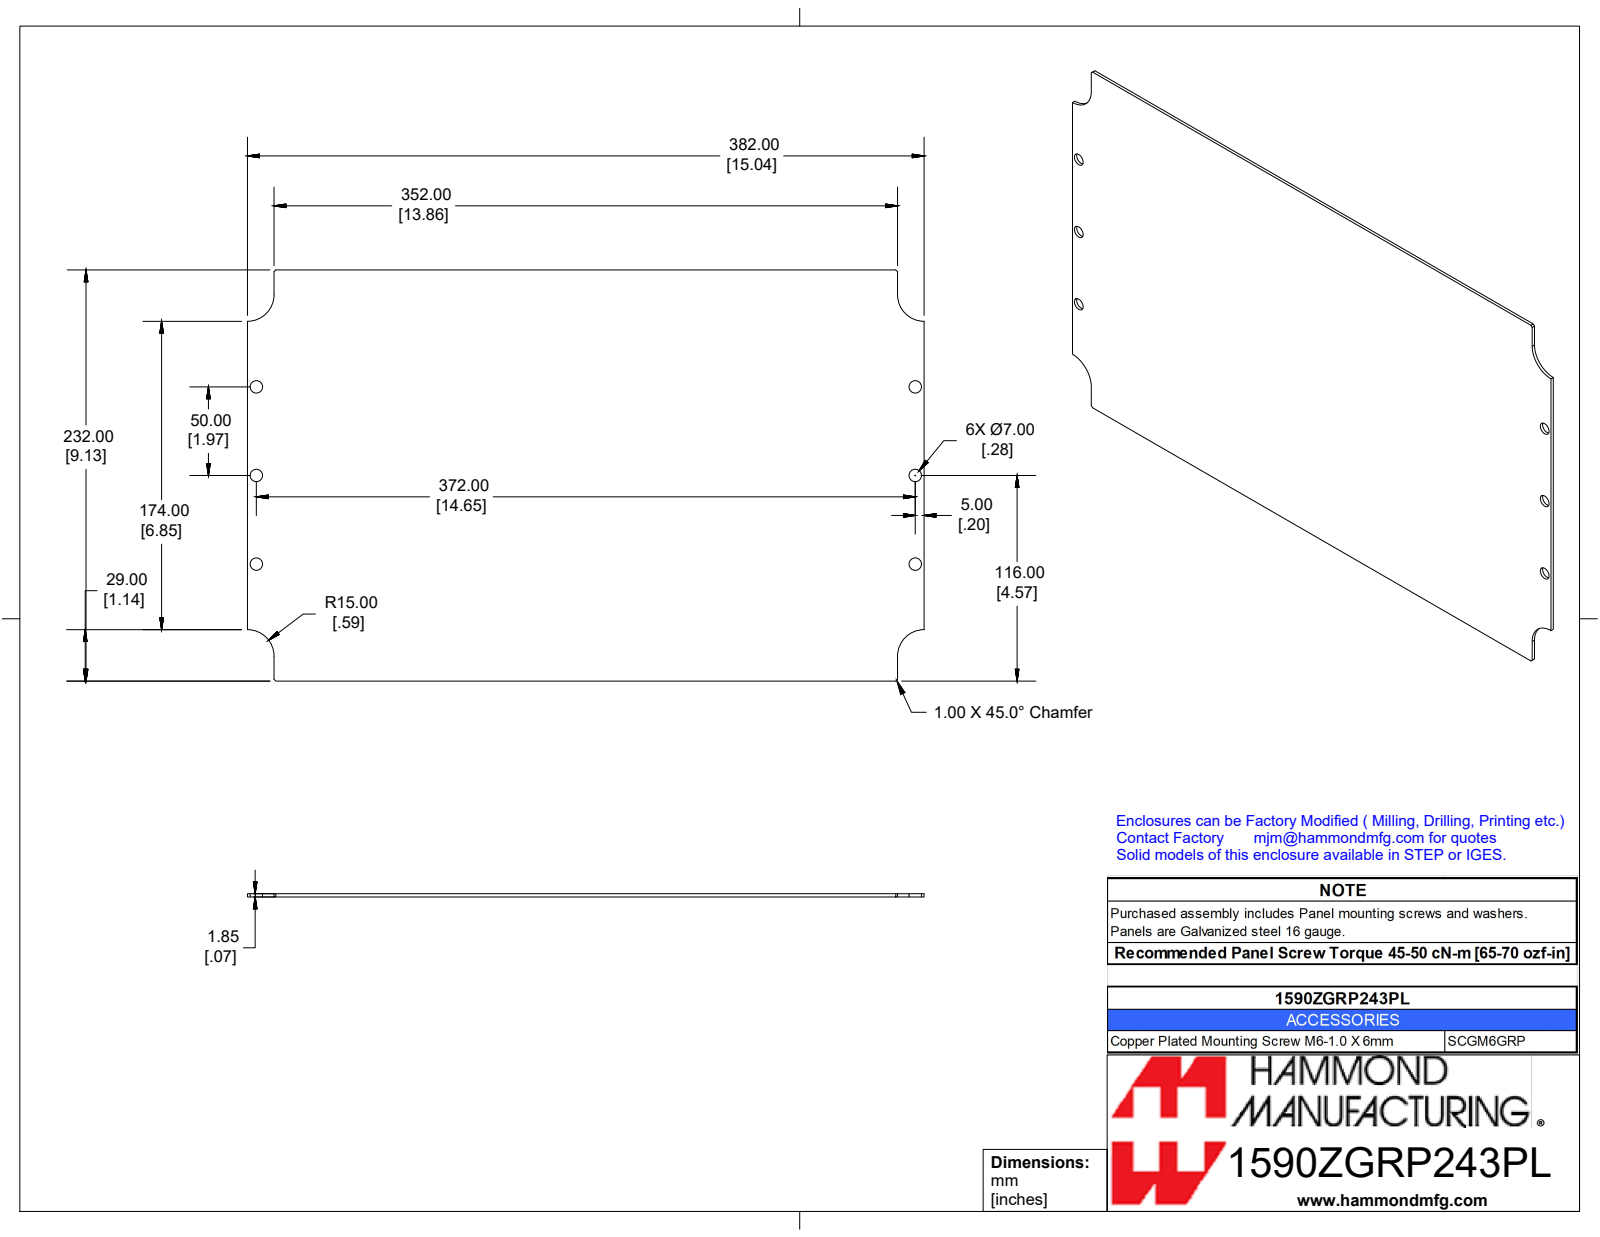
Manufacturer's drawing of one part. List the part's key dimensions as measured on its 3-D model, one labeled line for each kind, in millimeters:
Part name (STEP PRODUCT): 1590ZGRP243PL
STEP written by: SolidWorks 2019 (CONFIG_CONTROL_DESIGN)
Units: millimetres
Bodies: 1 solid, 24 faces (14 planar, 10 cylindrical, 0 other)
Overall size (bounding box): 382 × 232 × 1.9
Volume: 160 700 mm³ · Surface area: 176 100 mm²
Round holes (diameter × count): ⌀7 ×6
Partial cylindrical surfaces — rounded edges, fillets, slot ends (radius × count): R15 ×4
Main face-to-face distances: 1.9, 232, 382, 15, 367, 352, 411.5
Hole centre spacings: 50, 375.4, 372, 100, 385.2
